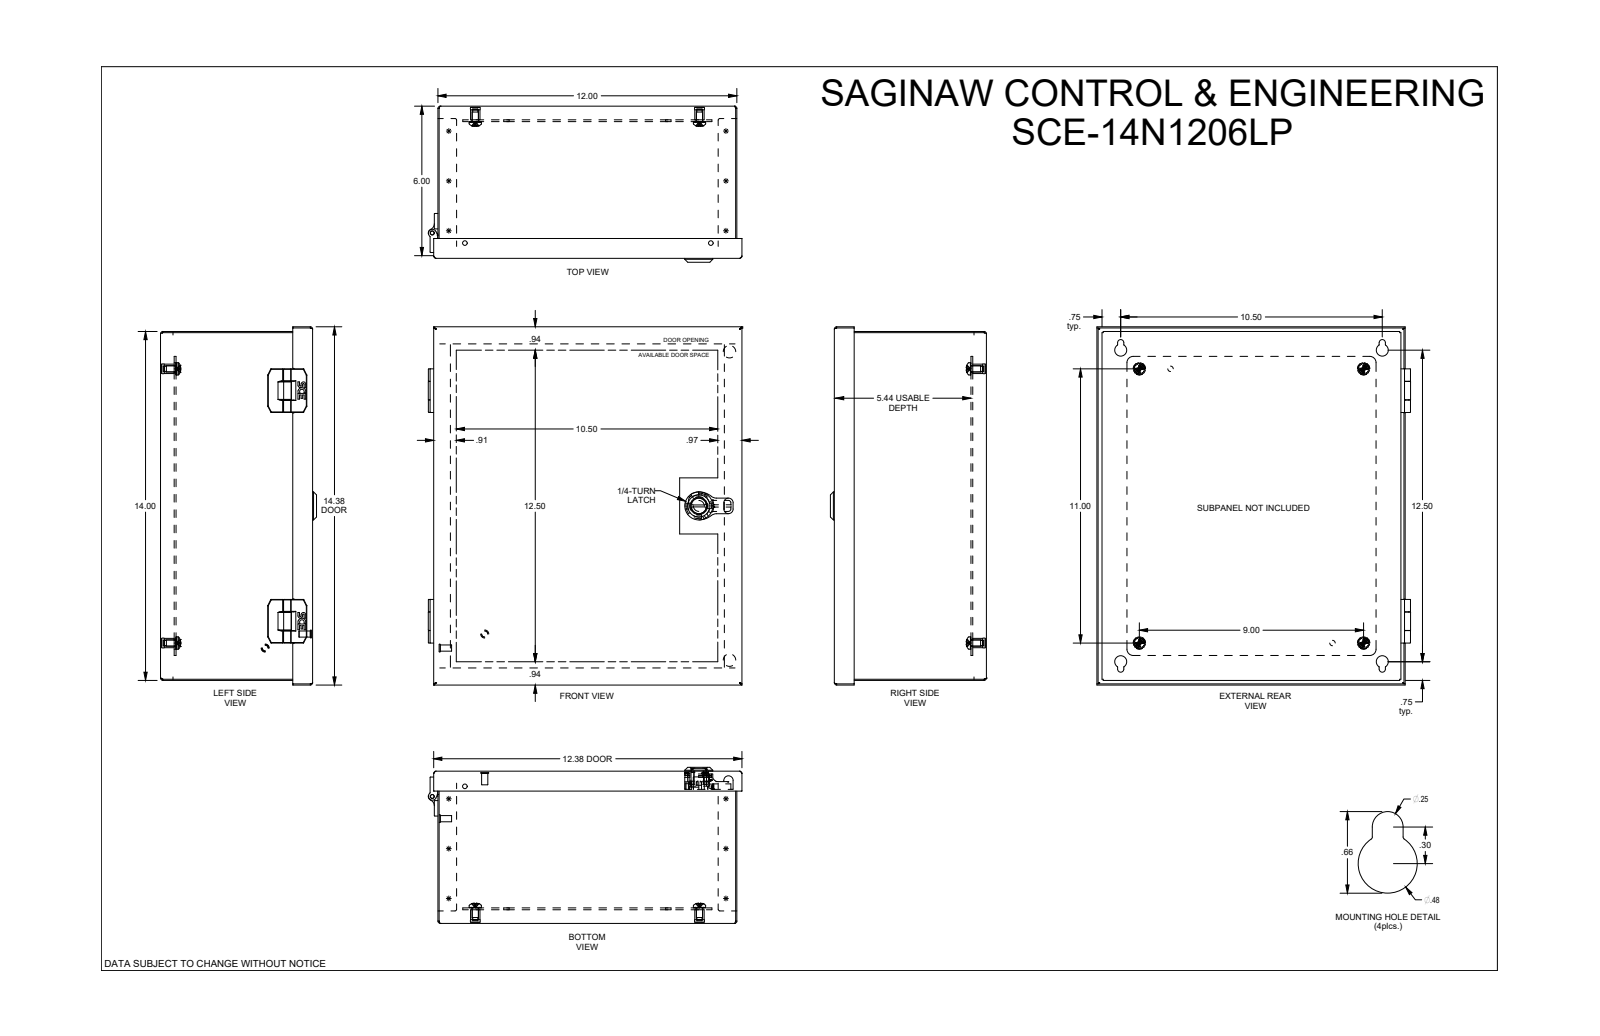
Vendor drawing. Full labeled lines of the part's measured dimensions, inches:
Part name (STEP PRODUCT): SCE-14N1206LP
STEP written by: SolidWorks 2019 (AUTOMOTIVE_DESIGN)
Units: inches
Bodies: 31 solids, 1529 faces (554 planar, 645 cylindrical, 330 other)
Overall size (bounding box): 14.383 × 12.593 × 6.263
Volume: 53.71 in³ · Surface area: 1 719 in²
Round holes (diameter × count): ⌀0.17 ×4, ⌀0.203 ×4, ⌀0.25 ×4, ⌀0.281 ×4, ⌀0.329 ×4, ⌀0.343 ×4, ⌀0.48 ×4, ⌀0.193 ×3, ⌀0.187 ×2, ⌀0.218 ×2, ⌀0.158 ×1, ⌀0.44 ×1
Round bosses / shafts (diameter × count): ⌀0.248 ×6, ⌀0.492 ×4, ⌀0.479 ×4, ⌀0.376 ×4, ⌀0.237 ×4, ⌀0.16 ×4, ⌀0.5 ×2, ⌀0.323 ×2
Partial cylindrical surfaces — rounded edges, fillets, slot ends (radius × count): R0.01 ×253, R0.02 ×95, R0.06 ×25, R0.015 ×24, R0.025 ×24, R0.055 ×6, R0.25 ×6, R0.125 ×4
Main face-to-face distances: 0.06, 6.047, 5.987, 6.107, 11.94, 13.94, 0.623, 0.563, 5.424, 5.484
Hole centre spacings: 1.061, 7.75, 9.779, 11.774, 15.269, 1.089, 1.091, 9.25
